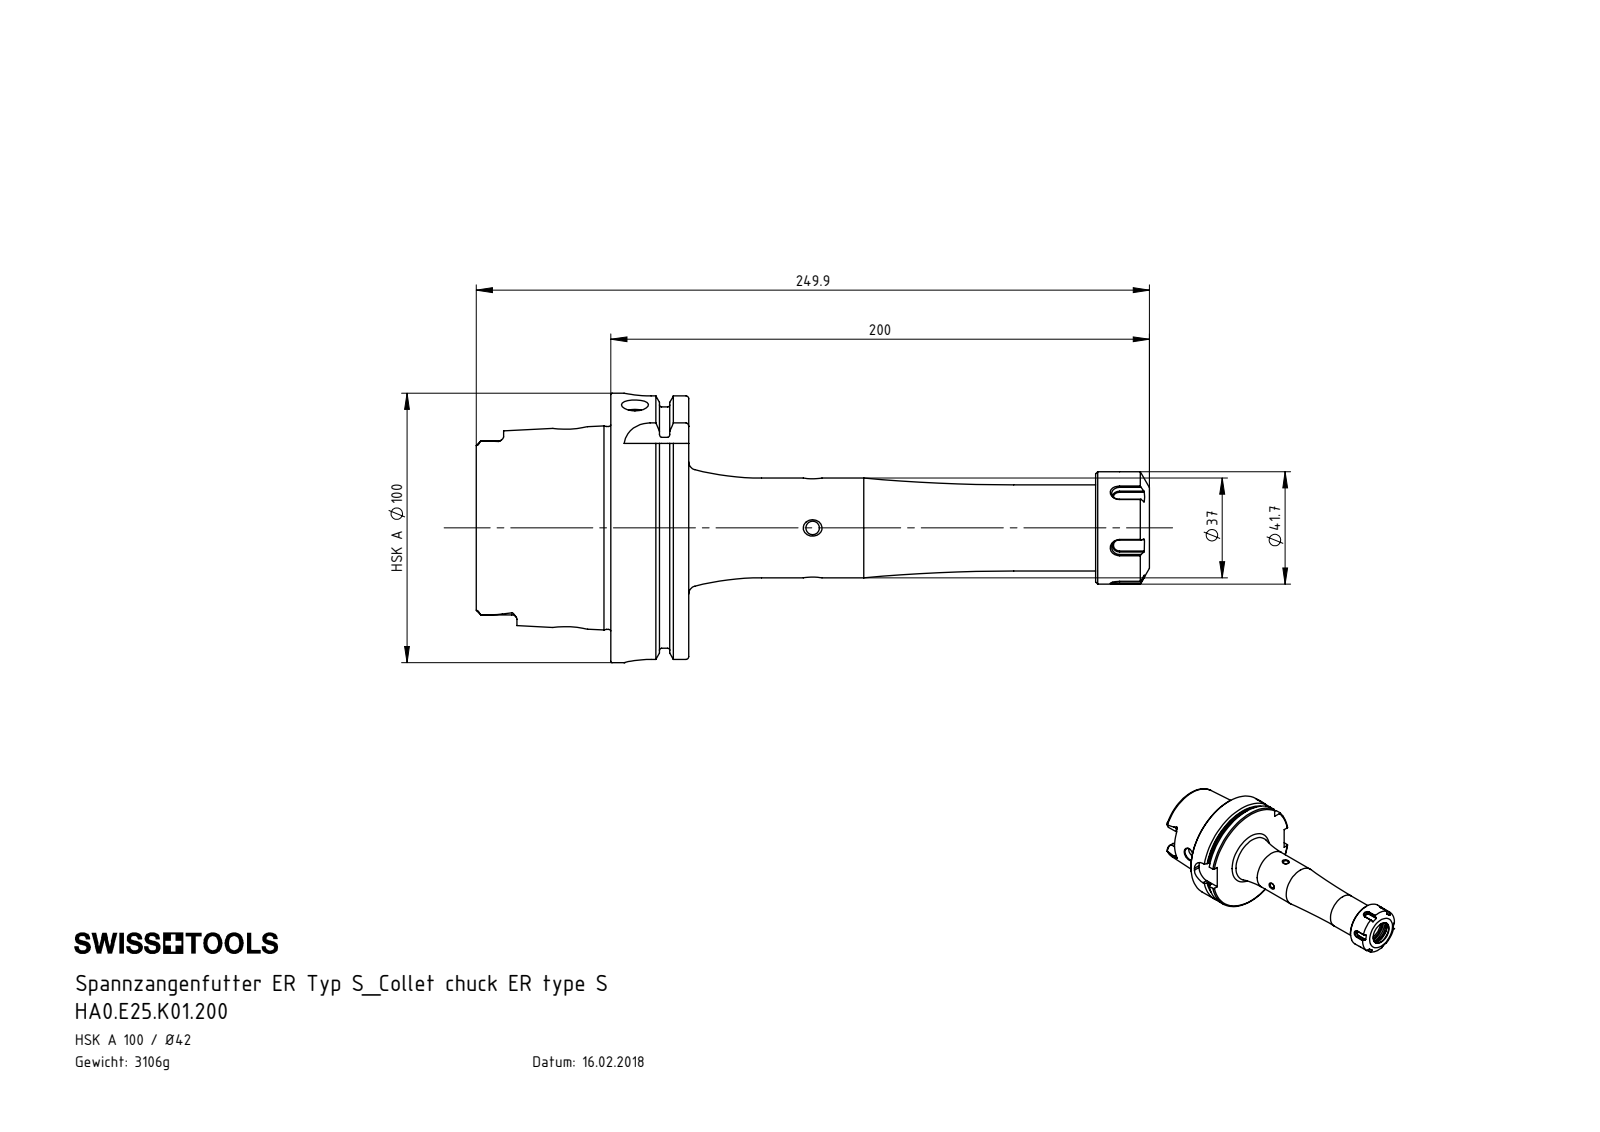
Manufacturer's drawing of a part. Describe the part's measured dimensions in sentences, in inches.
The part is named "HA0.E25.K01.200; ERU-AN5.K01.020_A; E25-ER1.001.020; HA0-E25.K01.200_C_Fertigbearbeitung". Its 3-D file was written by "SolidWorks 2017 (CONFIG_CONTROL_DESIGN)". It is 3 solids with 338 faces: 125 planar, 81 cylindrical and 132 other. Overall it measures 9.839 by 3.937 by 3.937 inches. Its volume is 24.14 cubic inches and its surface area 125.5 square inches. Round holes: 3 of diameter 0.394, 2 of diameter 0.197, 2 of diameter 0.472, 1 of diameter 0.236, 1 of diameter 0.433, 1 of diameter 0.709, 1 of diameter 0.823, 1 of diameter 0.886, 1 of diameter 1.024, 1 of diameter 1.201, 1 of diameter 1.28, 1 of diameter 2.087. Round bosses or shafts: 1 of diameter 3.937, 1 of diameter 3.62, 1 of diameter 2.963, 1 of diameter 1.642, 1 of diameter 1.457, 1 of diameter 1.26. Partial cylindrical surfaces (rounded edges, fillets, slot ends): 6 of radius 0.075, 4 of radius 0.192, 4 of radius 0.394, 2 of radius 0.479. The main face-to-face distances are 1.14, 0.49, 0.65, 1.965, 2.455, 3.104, 9.051, 7.087, 6.596, 5.947. The hole center spacings are 2.675, 3.541.
